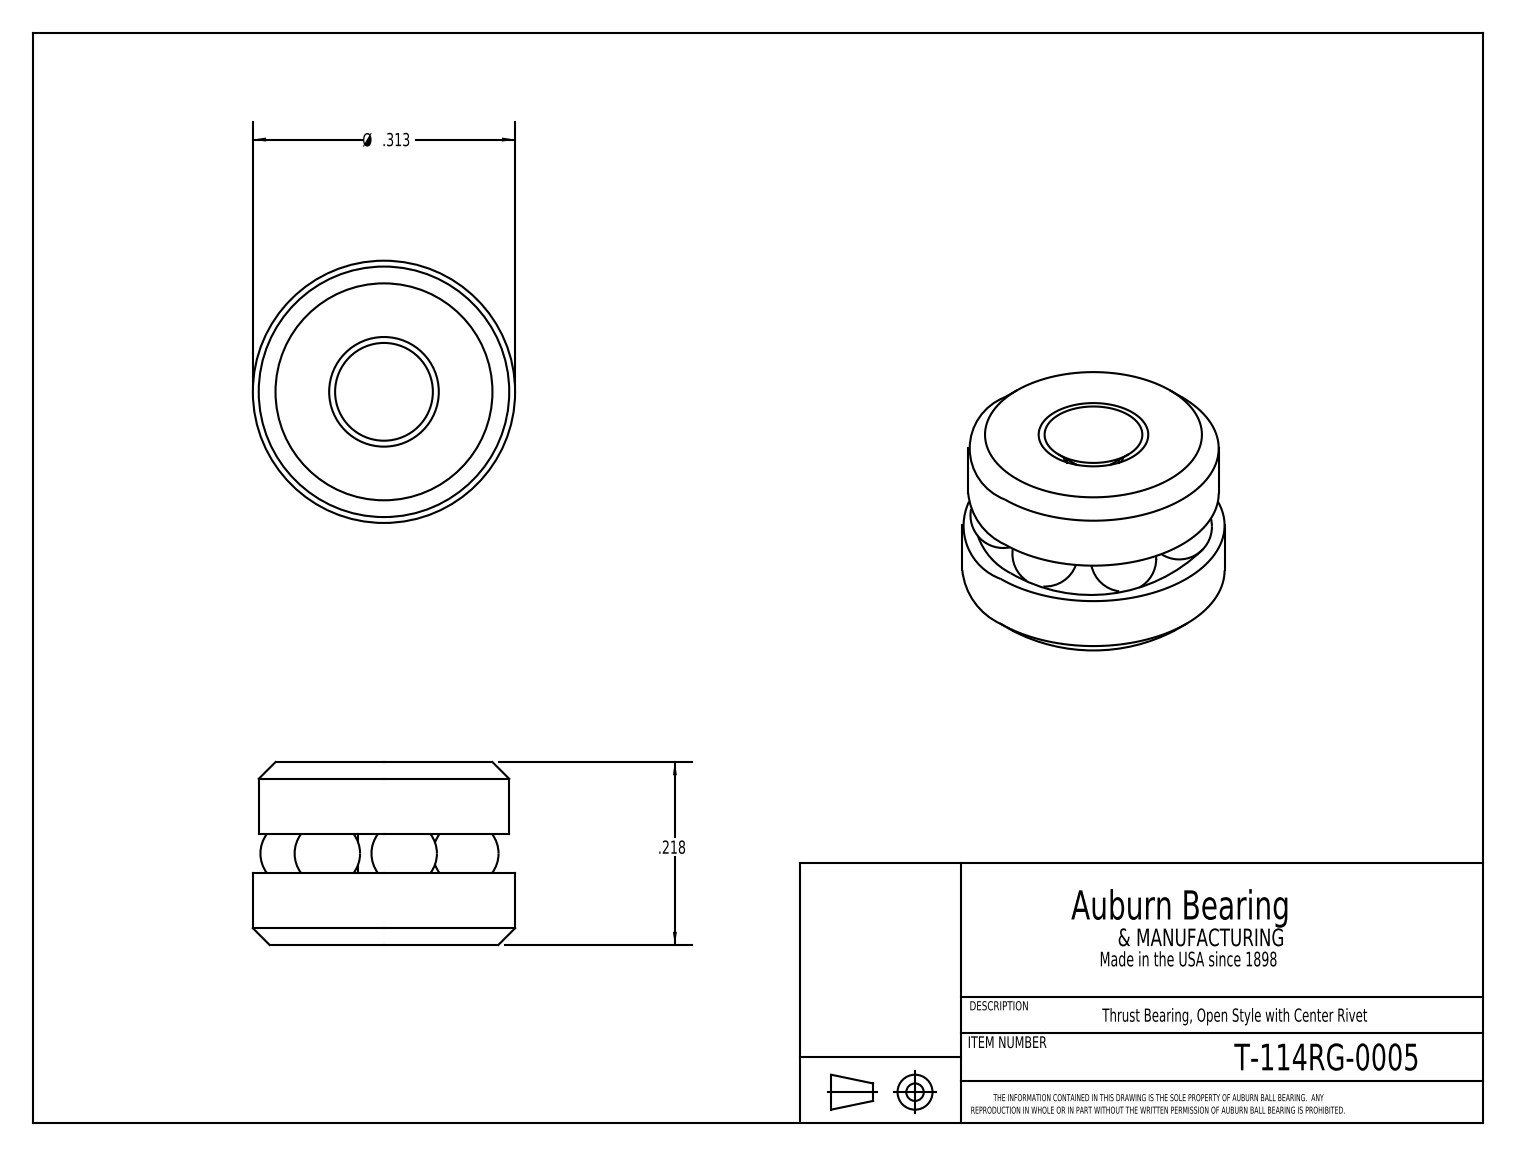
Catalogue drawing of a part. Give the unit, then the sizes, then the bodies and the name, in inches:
Units: inches
Overall size (bounding box): 0.313 × 0.313 × 0.218
Round holes (diameter × count): ⌀0.072 ×1
Round bosses / shafts (diameter × count): ⌀0.313 ×1, ⌀0.299 ×1, ⌀0.062 ×1
Main face-to-face distances: 0.218, 0.085, 0.133, 0.132, 0.047, 0.086
Volume: 0.013 in³ · Surface area: 0.673 in²
Bodies: 10 solids, 28 faces (8 planar, 5 cylindrical, 15 other)
Part name (STEP PRODUCT): T-114RG_T-114RG-0005
STEP written by: SolidWorks 2016 (CONFIG_CONTROL_DESIGN)
